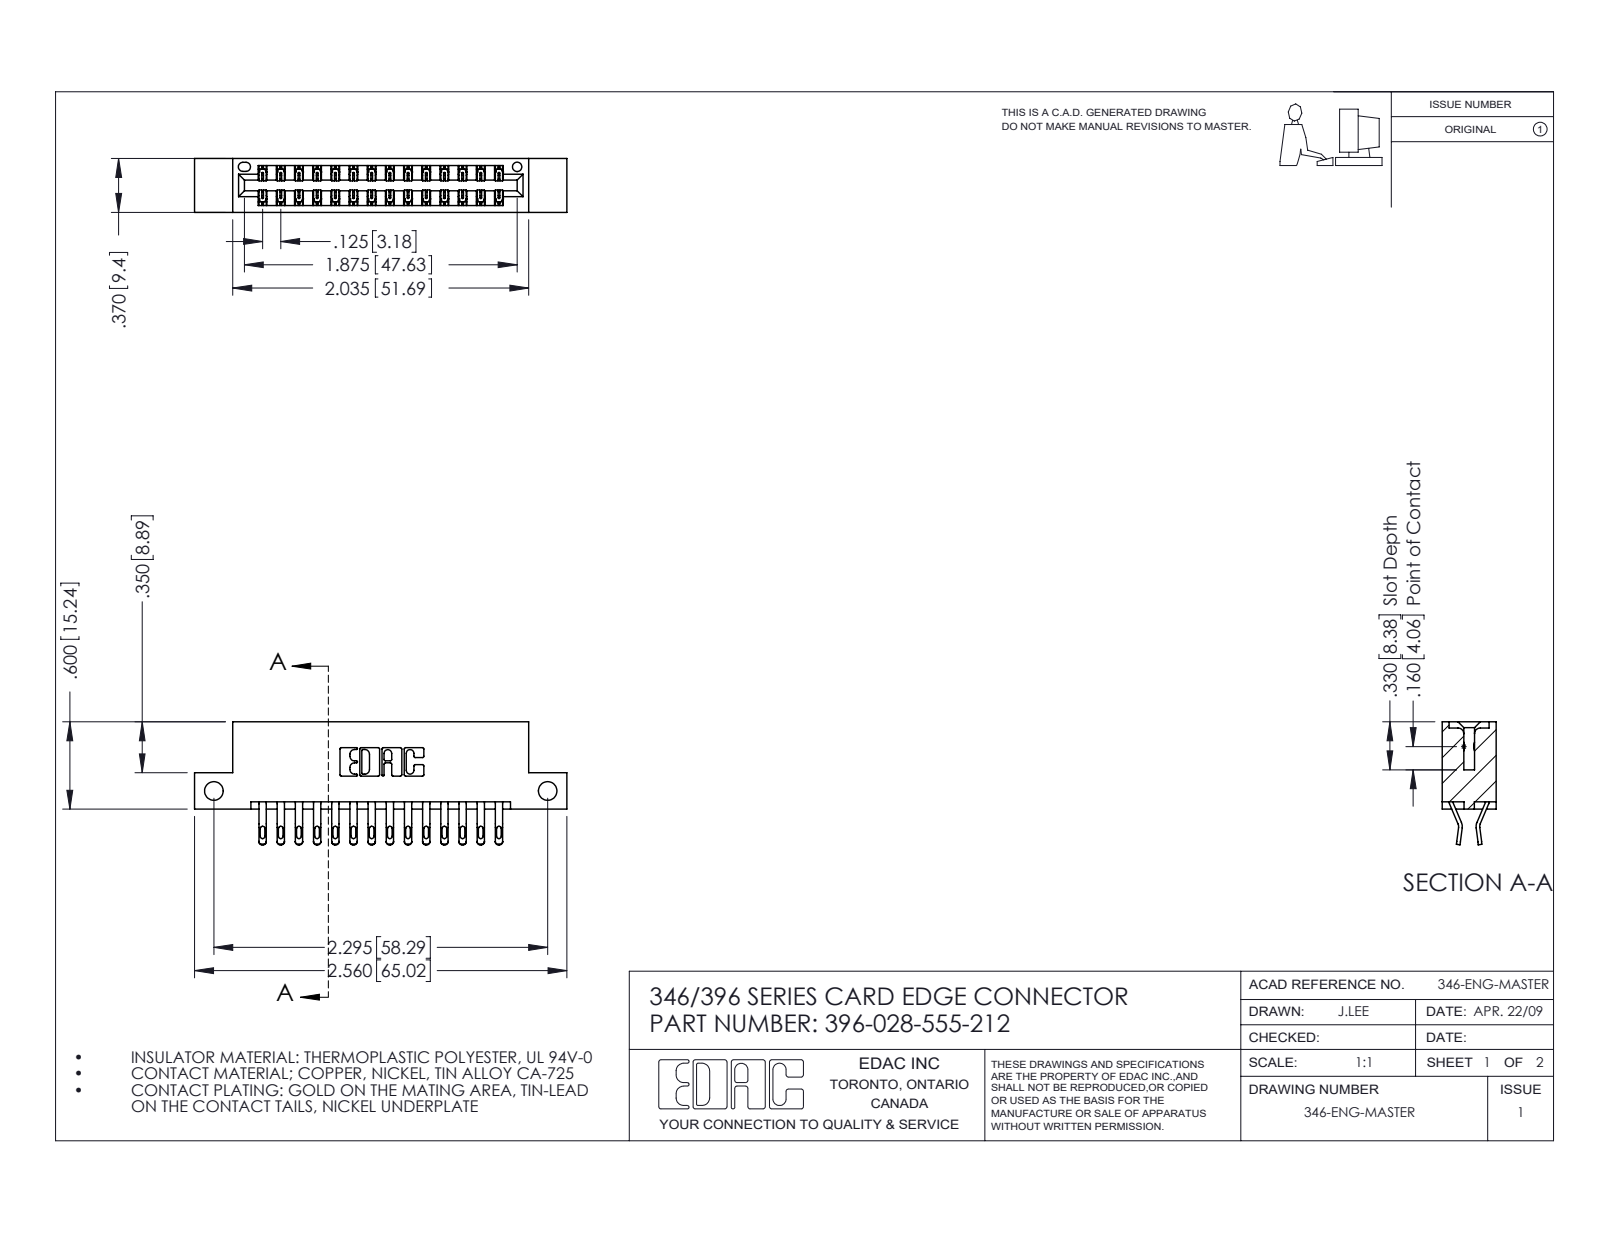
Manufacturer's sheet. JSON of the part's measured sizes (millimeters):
{"part_name": "396-028-555-212; 345-292-001_555 Tail; 346 Part_Flush Mounting Lugs - Side Mount", "step_written_by": "SolidWorks 2016 (CONFIG_CONTROL_DESIGN)", "units": "millimeters", "bodies": {"solids": 29, "faces": 1746, "planar": 1000, "cylindrical": 746, "other": 0}, "overall_size": [65, 21.5, 9.4], "volume_mm3": 6110, "surface_area_mm2": 8123, "round_holes": [[3.3, 2], [1.6, 1]], "partial_cylinders_radius": [[0.4, 56], [0.5, 56], [0.2, 42], [0.3, 22], [0.2, 6], [0.8, 6], [0.7, 3], [0.3, 2]], "face_to_face_distances": [6.4, 1.2, 8.2, 9.4, 0.6, 1.8, 7.6, 7, 3.8, 5.6], "hole_center_spacings": [58.3]}
